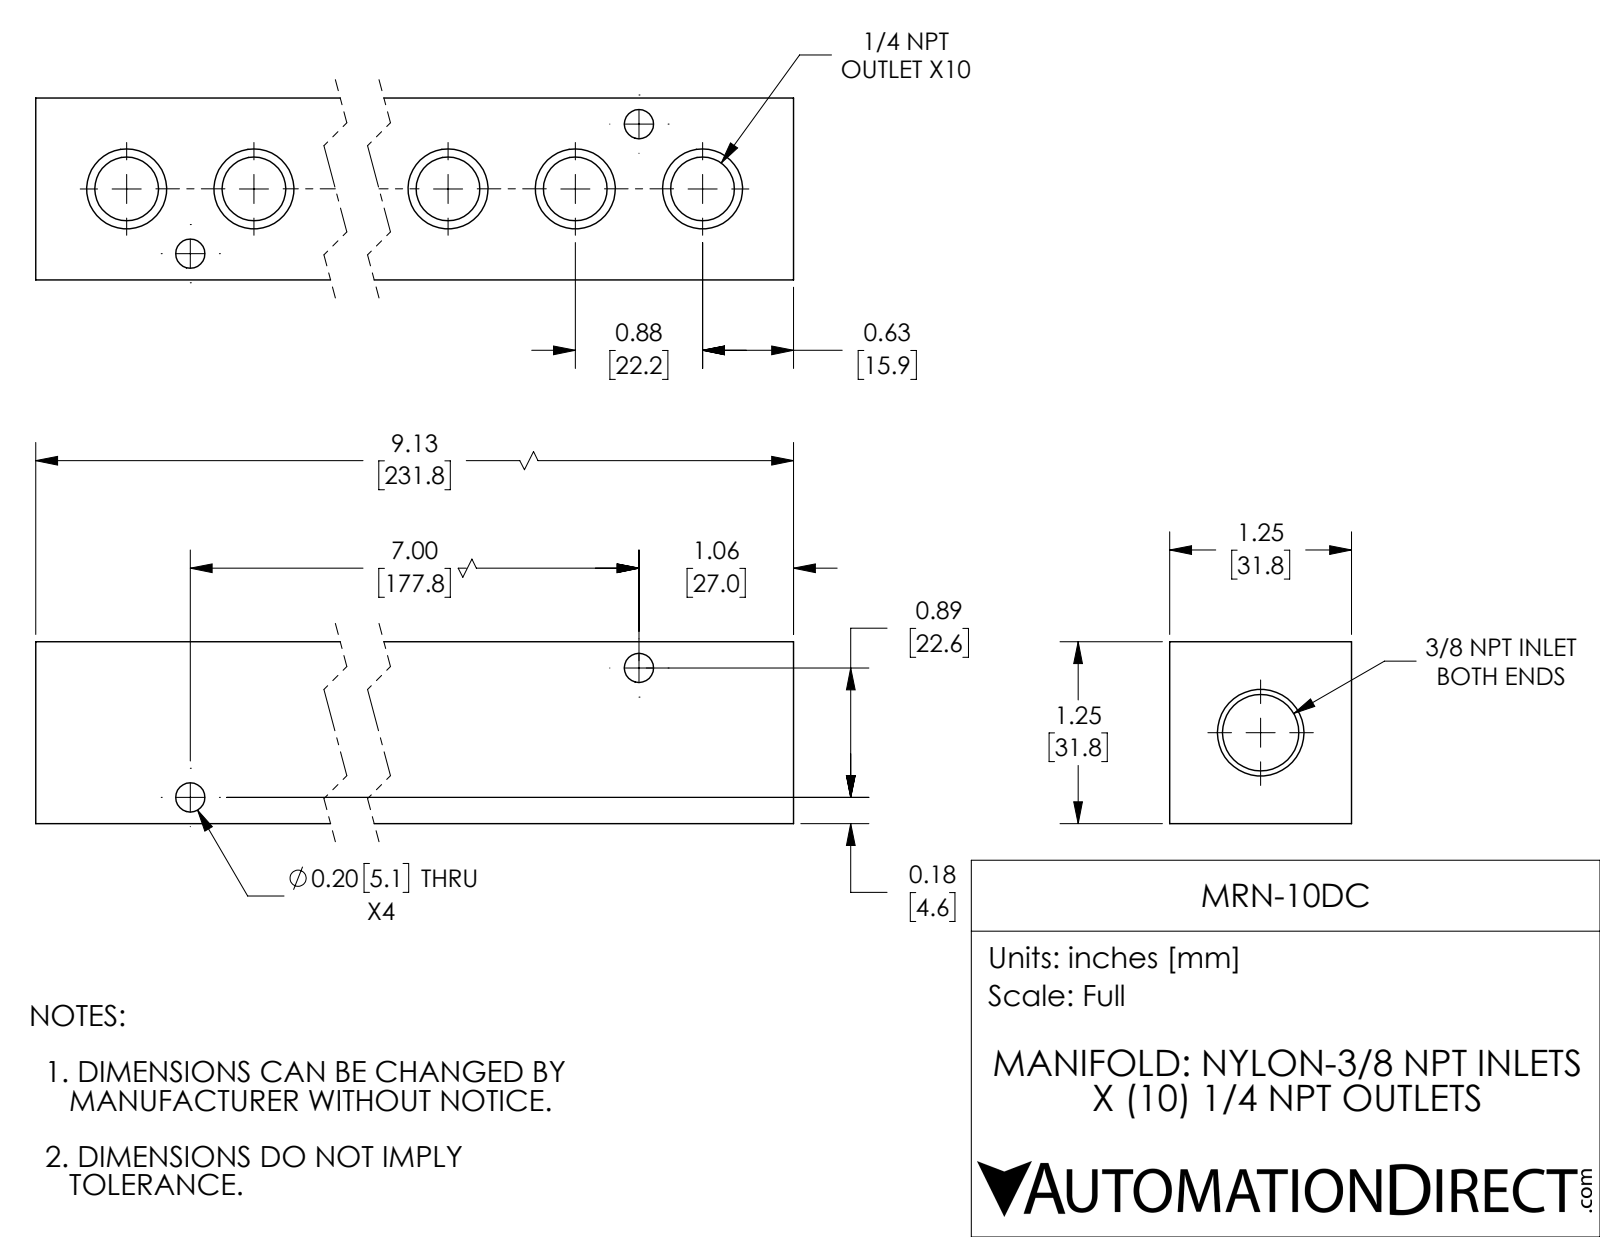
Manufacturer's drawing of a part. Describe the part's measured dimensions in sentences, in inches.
The part is named "MRN-10DC". Its 3-D file was written by "SolidWorks 2018 (AUTOMOTIVE_DESIGN)". It is 1 solid with 68 faces: 6 planar, 38 cylindrical and 24 other. Overall it measures 9.125 by 1.25 by 1.25 inches. Its volume is 11.52 cubic inches and its surface area 68.01 square inches. Round holes: 10 of diameter 0.438, 4 of diameter 0.201, 1 of diameter 0.525. The main face-to-face distances are 1.25, 9.125. The hole center spacings are 1.75, 0.875, 3.5, 0.624, 0.875, 2.625, 2.625, 4.375.
